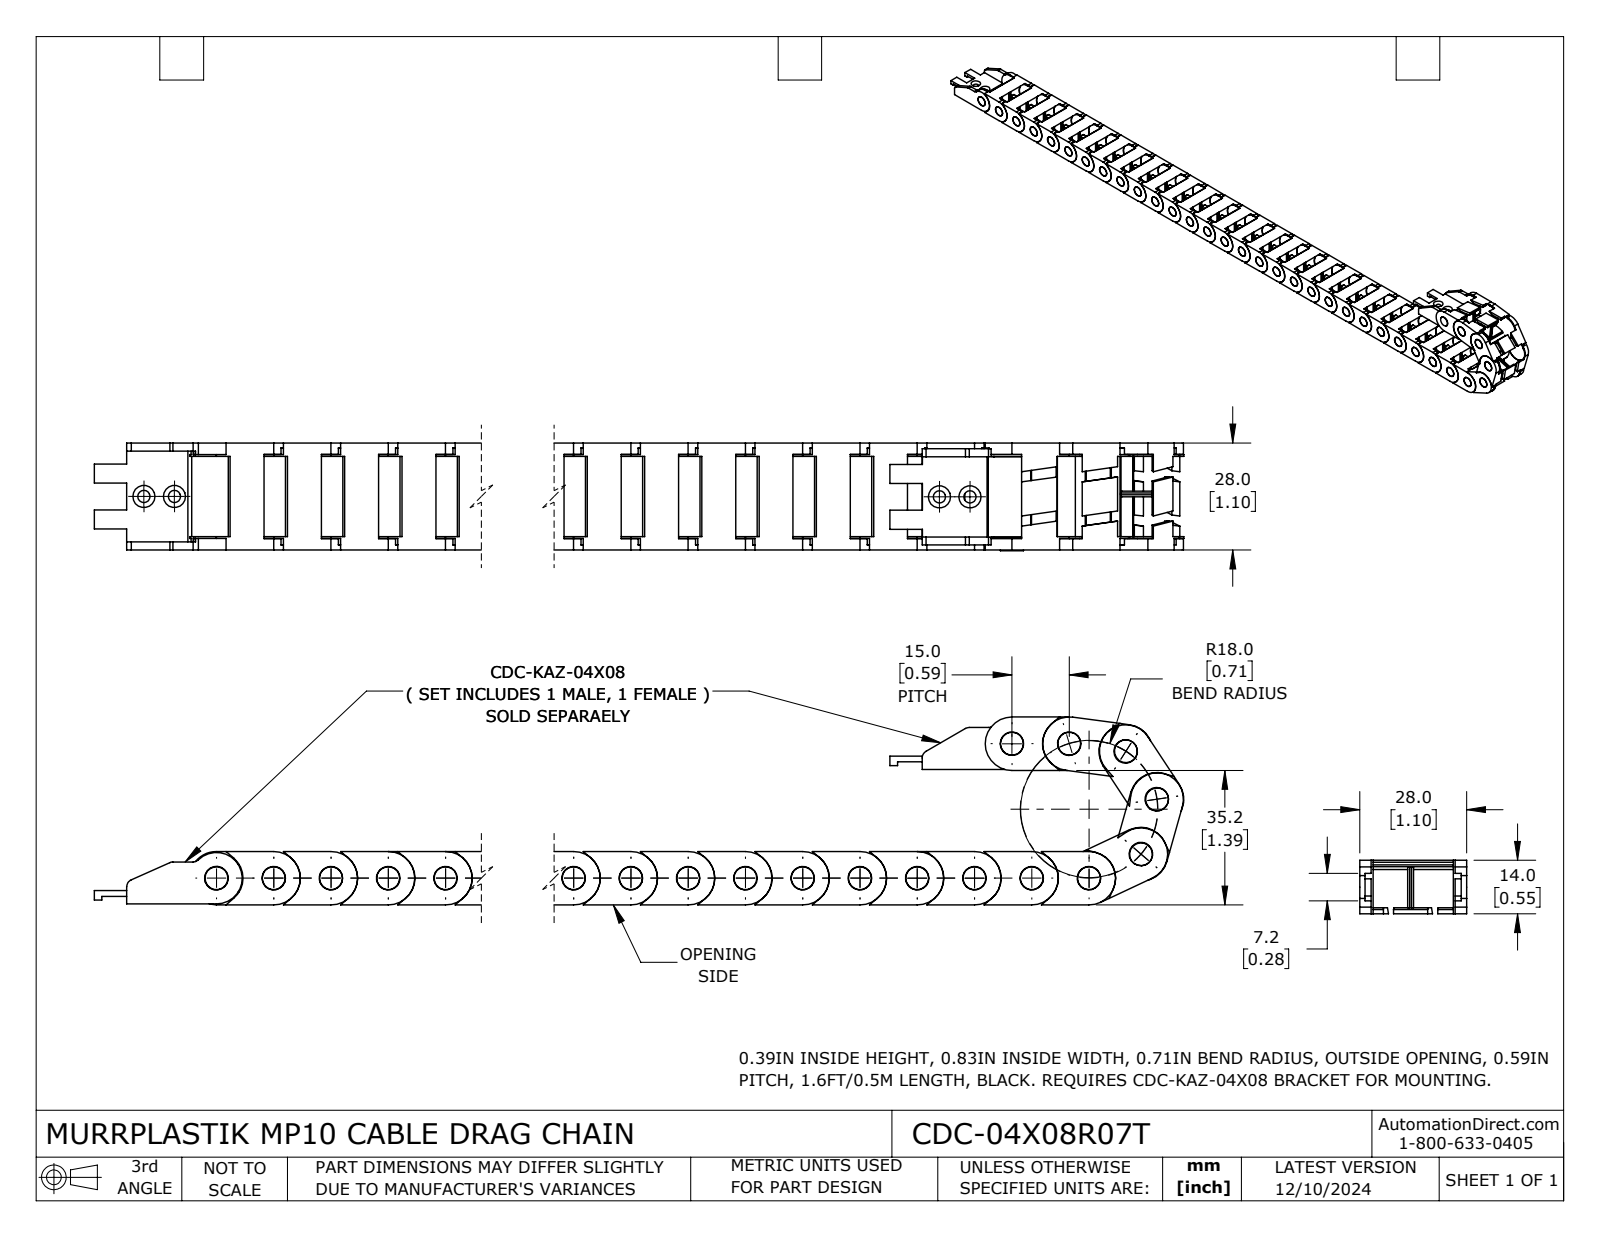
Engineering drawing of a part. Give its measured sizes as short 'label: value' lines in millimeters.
name: CDC-04X08R07T
written by: SolidWorks 2024 (AUTOMOTIVE_DESIGN)
unit: mm
bodies: 34 solids, 2797 faces (1892 planar, 901 cylindrical, 4 other)
size: 476.8 × 49.2 × 28.2
volume: 69 990 mm³; area: 98 000 mm²
holes: 32× ⌀6.1, 4× ⌀3.2, 1× ⌀6.2
bosses: 33× ⌀6, 28× ⌀14
rounds: 288× R0.5, 36× R7, 32× R3.6, 32× R11.6, 8× R7, 6× R2, 2× R1, 2× R6.8
face distances: 3.5, 24.5, 28, 14, 1.6, 21, 23.2, 2.2, 1.3, 26.7
hole spacings: 15, 30, 45, 60, 75, 90, 105, 120
